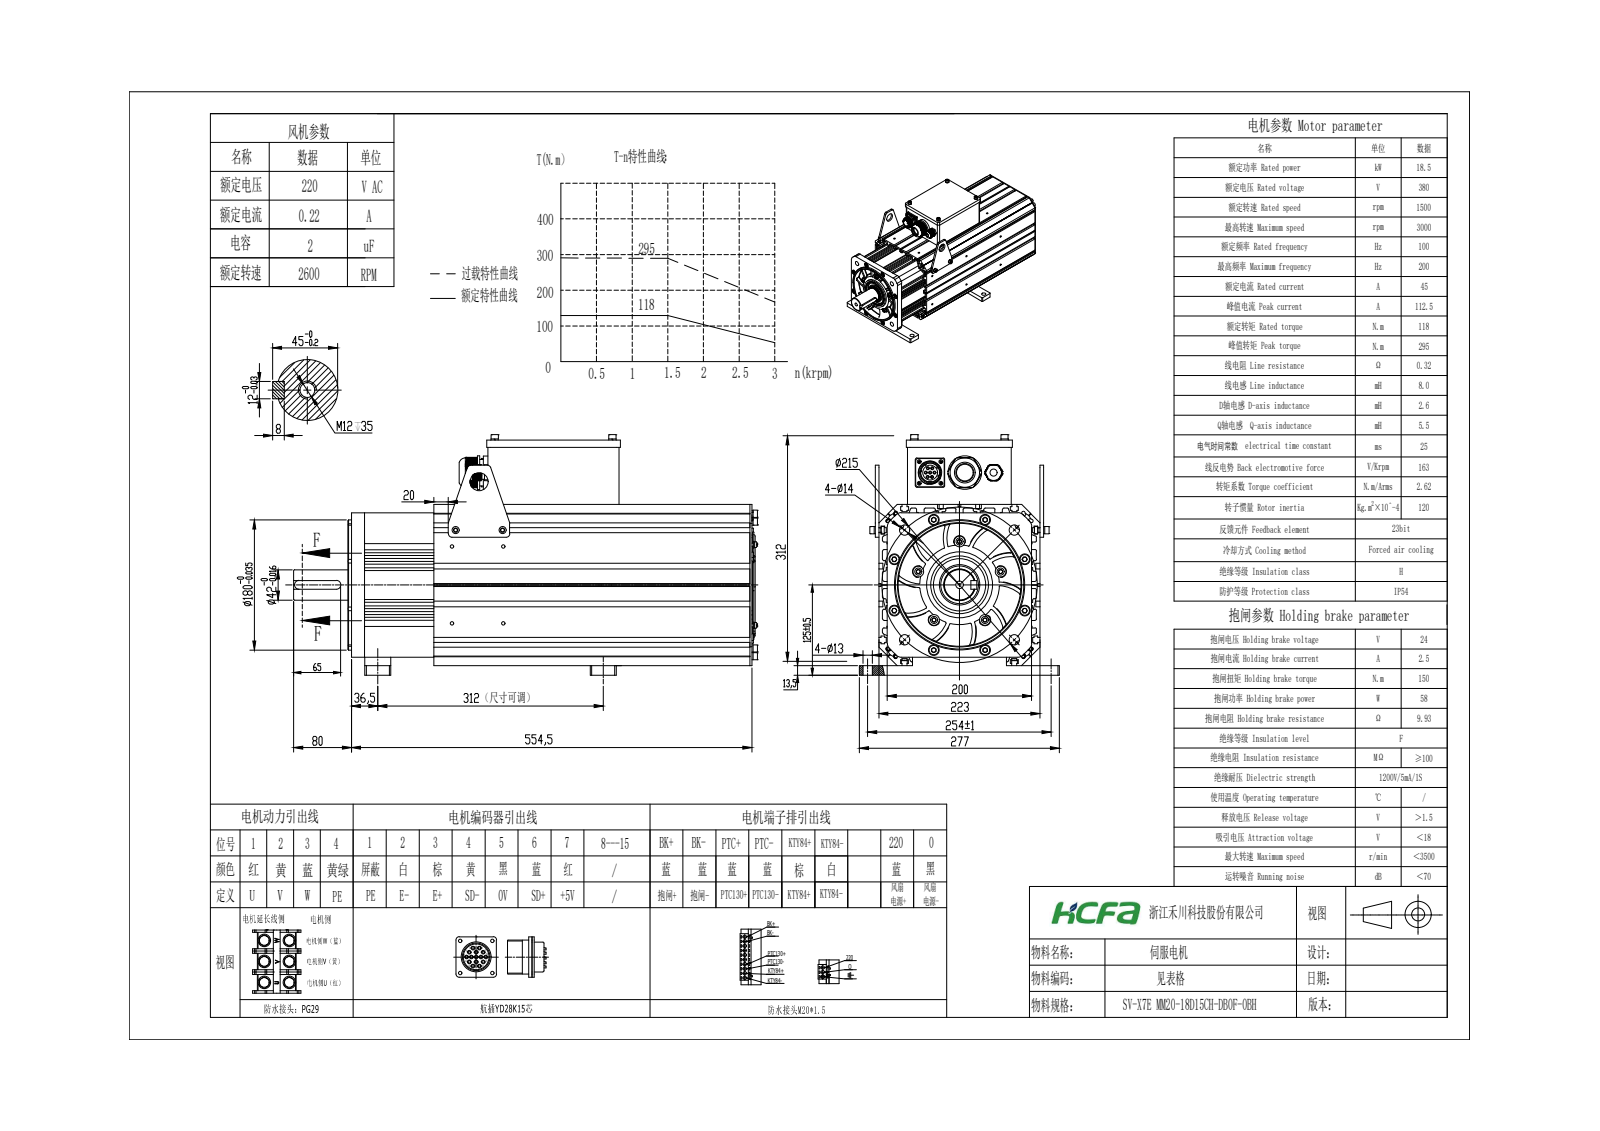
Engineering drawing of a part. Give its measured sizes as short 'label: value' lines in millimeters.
name: 18.5KW抱闸
written by: SolidWorks 2021 (CONFIG_CONTROL_DESIGN)
unit: mm
bodies: 91 solids, 4316 faces (2345 planar, 1227 cylindrical, 744 other)
size: 642.1 × 333.1 × 277
volume: 7 056 000 mm³; area: 2 709 000 mm²
holes: 24× ⌀5, 17× ⌀6.8, 15× ⌀6.68, 14× ⌀9, 11× ⌀6.5, 10× ⌀15, 8× ⌀3.5, 8× ⌀8, 7× ⌀4.2, 6× ⌀4.5, 5× ⌀14, 4× ⌀2.5
bosses: 24× ⌀2, 17× ⌀10, 17× ⌀6, 15× ⌀9.88, 14× ⌀8, 11× ⌀4, 10× ⌀13, 8× ⌀3
rounds: 84× R2, 24× R0.5, 20× R5, 15× R3, 14× R2.5, 12× R10, 8× R1.5, 8× R2.41
face distances: 223, 2.5, 5, 218, 6.5, 11.5, 211.5, 206.5, 8, 198.5
hole spacings: 130.5, 168.38, 106.4, 261, 1.77, 41.18, 42.89, 72.86
